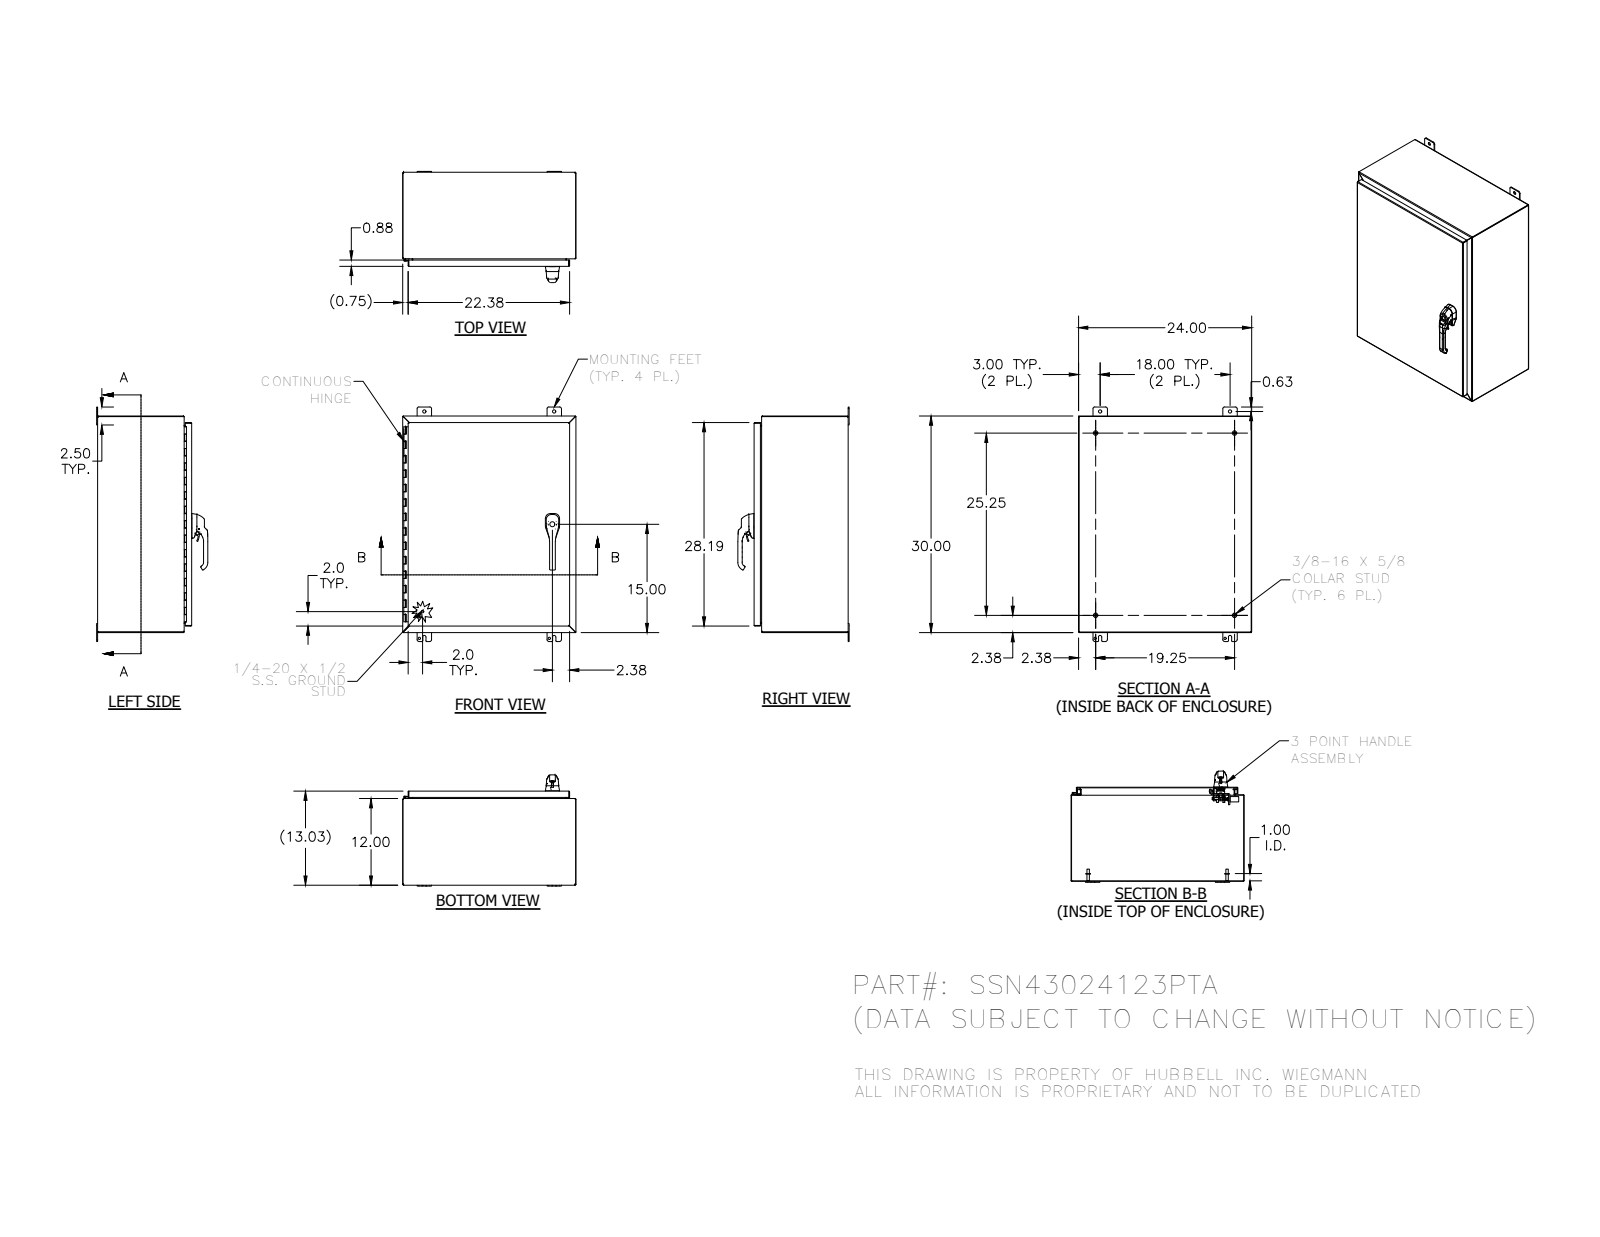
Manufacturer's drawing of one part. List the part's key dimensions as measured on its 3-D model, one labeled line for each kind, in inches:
Part name (STEP PRODUCT): 328139P; LOCK-NUT_AF0; 1000-277-01; SSN430243PTALID (+8 more)
STEP written by: SolidWorks 2014 (AUTOMOTIVE_DESIGN)
Units: inches
Bodies: 56 solids, 3140 faces (1047 planar, 1306 cylindrical, 787 other)
Overall size (bounding box): 32.5 × 24 × 15.408
Volume: 249 in³ · Surface area: 6 478 in²
Round holes (diameter × count): ⌀0.262 ×8, ⌀0.187 ×4, ⌀0.313 ×4, ⌀0.438 ×4, ⌀0.213 ×3, ⌀0.281 ×3, ⌀0.241 ×2, ⌀0.25 ×2, ⌀0.252 ×2, ⌀0.315 ×2, ⌀0.4 ×2, ⌀0.402 ×2
Round bosses / shafts (diameter × count): ⌀0.625 ×4, ⌀0.33 ×4, ⌀0.236 ×3, ⌀1 ×2, ⌀0.563 ×2, ⌀0.533 ×2, ⌀0.531 ×2, ⌀0.5 ×2
Partial cylindrical surfaces — rounded edges, fillets, slot ends (radius × count): R0.02 ×172, R0.012 ×113, R0.125 ×26, R0.031 ×24, R0.019 ×21, R0.105 ×20, R0.25 ×20, R0.025 ×16
Main face-to-face distances: 0.074, 12.959, 23.926, 12.885, 13.033, 29.926, 23.852, 24, 30, 29.852
Hole centre spacings: 0.38, 0.492, 0.76, 1.593, 18, 30, 34.986, 0.886
